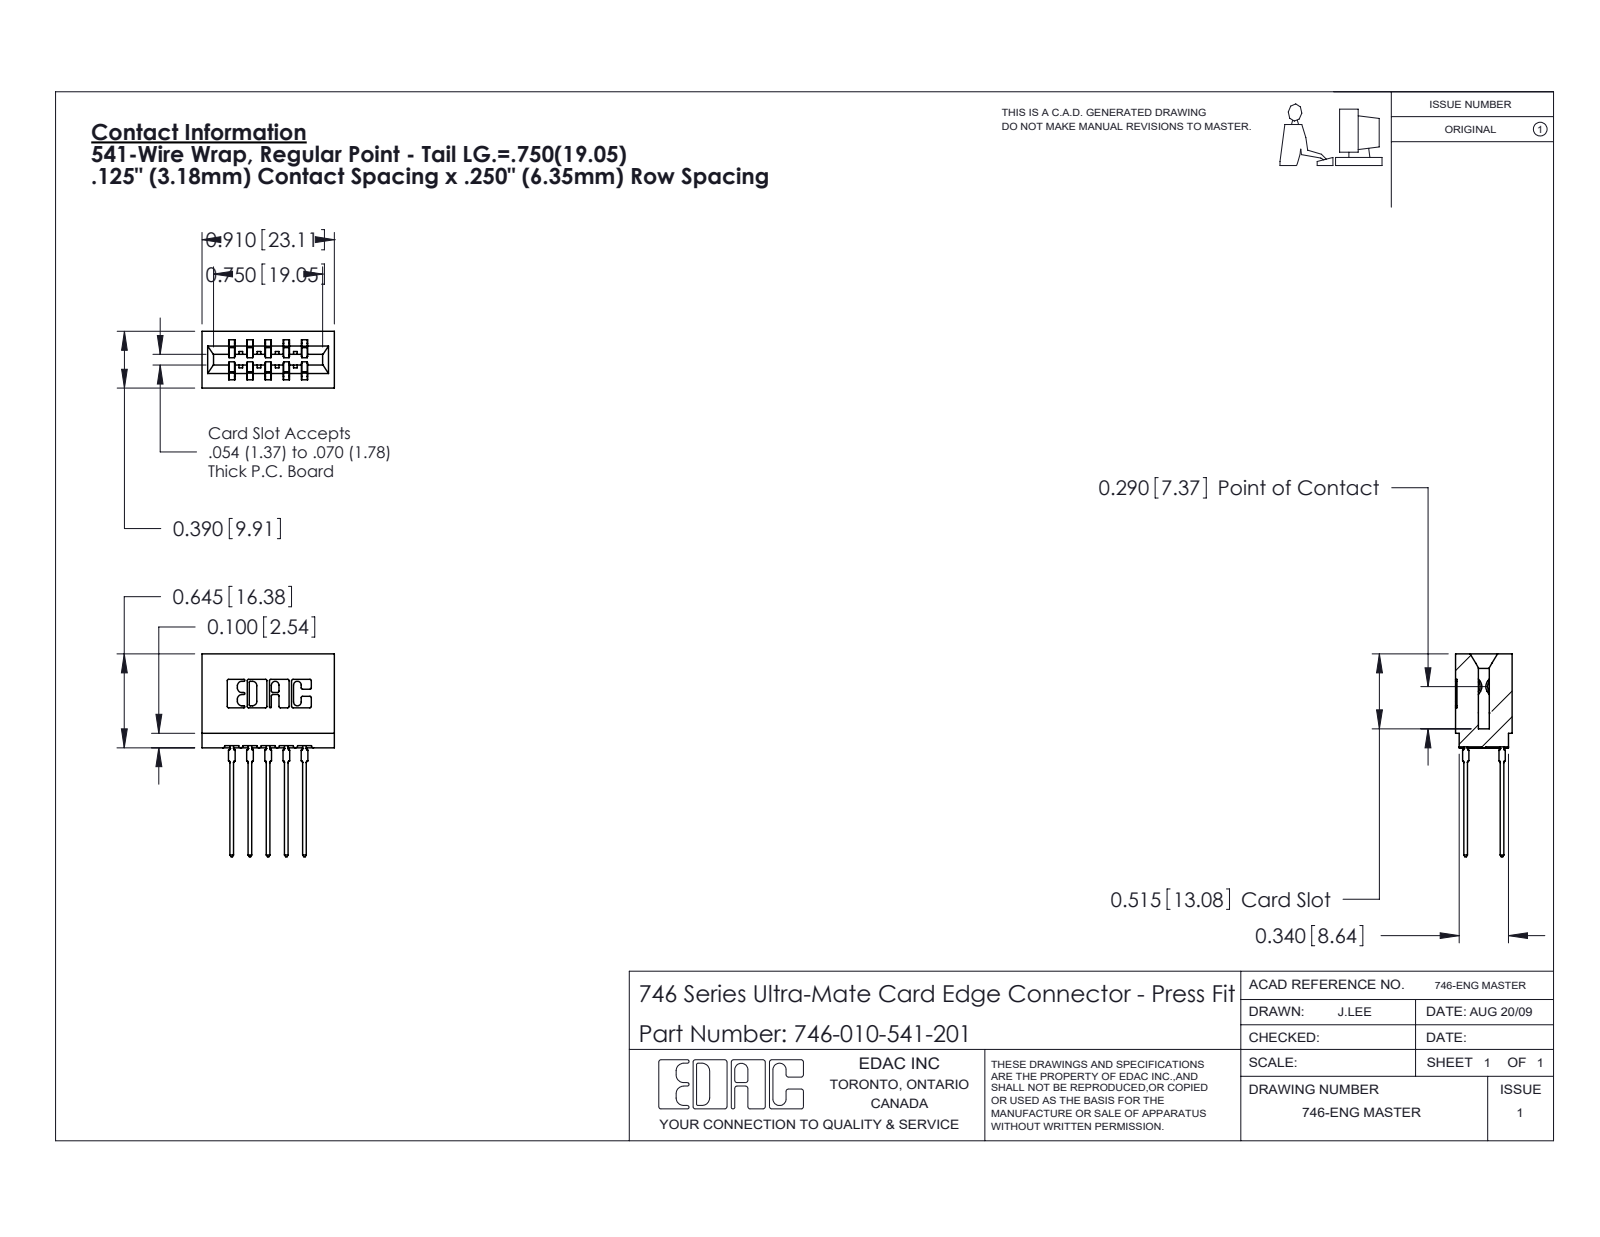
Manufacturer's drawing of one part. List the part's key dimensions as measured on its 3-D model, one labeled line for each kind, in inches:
Part name (STEP PRODUCT): 746-292-001_541; 746 Part_.515 Slot Depth - 01; 746-010-541-201
STEP written by: SolidWorks 2020 (CONFIG_CONTROL_DESIGN)
Units: inches
Bodies: 11 solids, 992 faces (515 planar, 217 cylindrical, 260 other)
Overall size (bounding box): 1.394 × 0.91 × 0.39
Volume: 0.169 in³ · Surface area: 6.143 in²
Partial cylindrical surfaces — rounded edges, fillets, slot ends (radius × count): R0.01 ×22, R0.021 ×20, R0.005 ×8, R0.011 ×8, R0.007 ×6, R0.015 ×6, R0.031 ×6, R0.026 ×3
Main face-to-face distances: 0.25, 0.057, 0.333, 0.042, 0.125, 0.125, 0.025, 0.083, 0.307, 0.39
